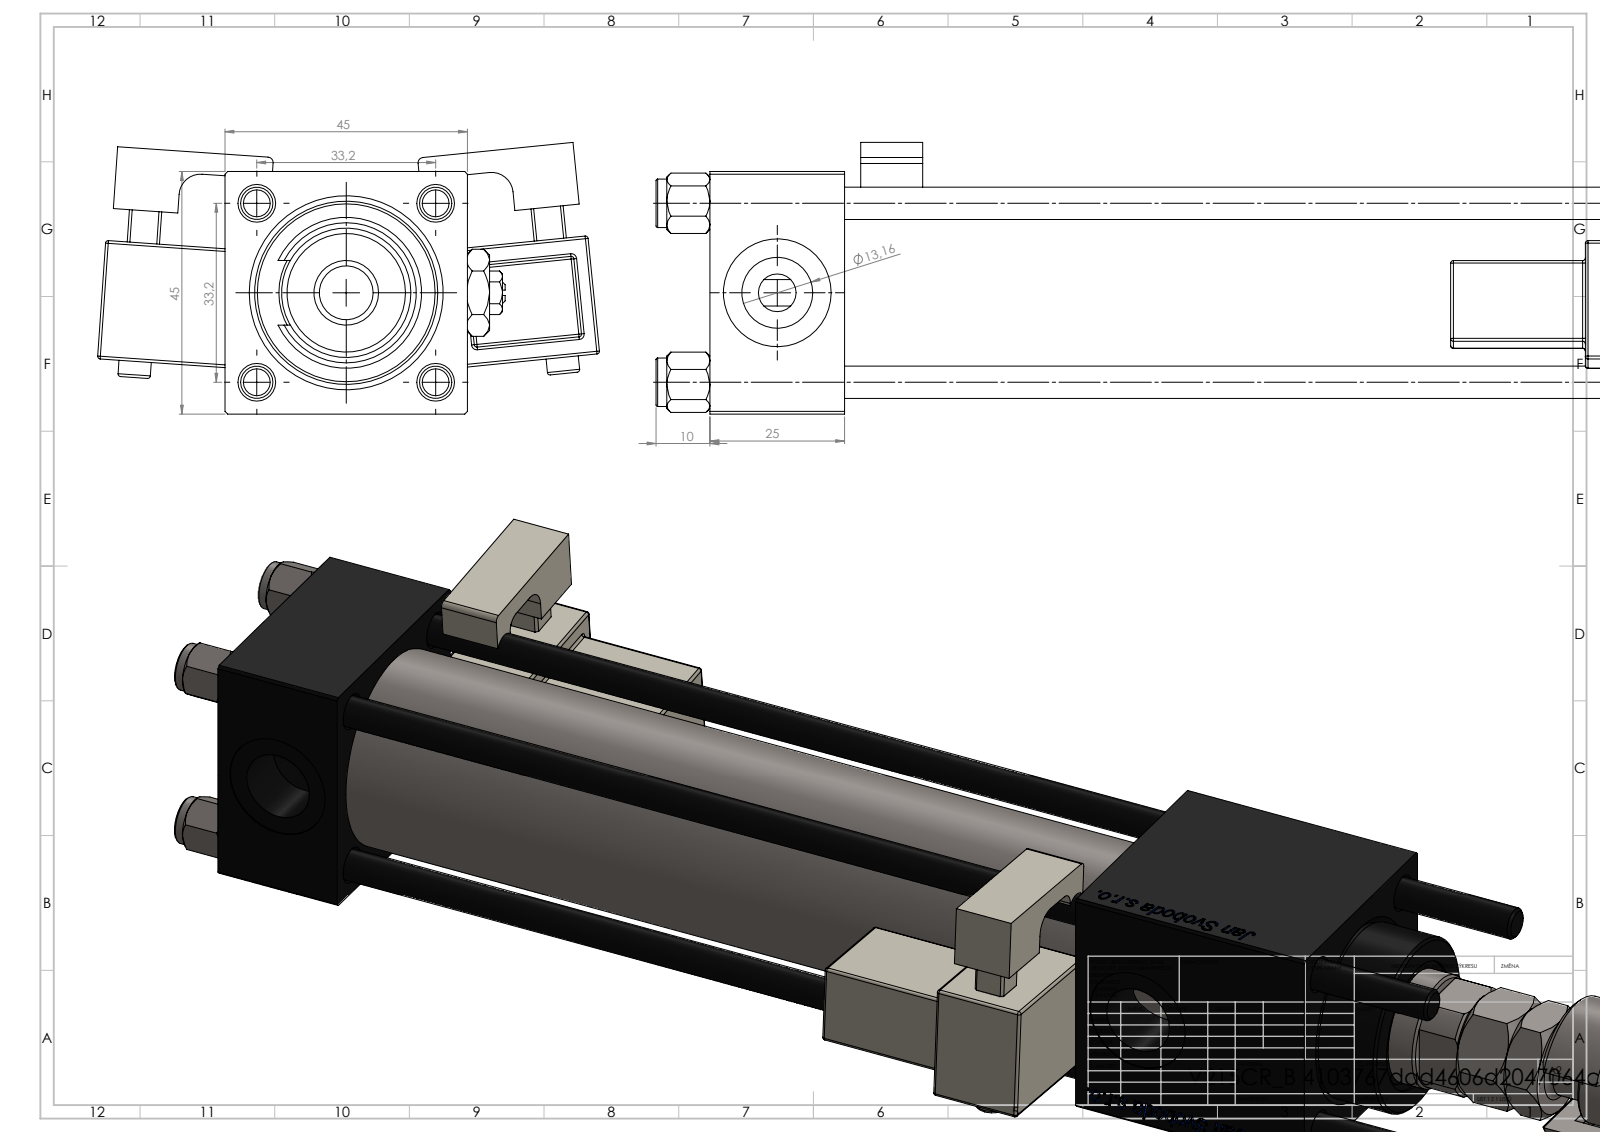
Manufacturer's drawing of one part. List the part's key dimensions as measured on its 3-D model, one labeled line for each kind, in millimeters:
Part name (STEP PRODUCT): V215CR_B_TYCINKA; FEMALE_PART_FOR_DFA; NUT_M5_B; V215CR_VCP_B (+5 more)
STEP written by: SolidWorks 2019 (CONFIG_CONTROL_DESIGN)
Units: millimetres
Bodies: 17 solids, 1499 faces (568 planar, 161 cylindrical, 770 other)
Overall size (bounding box): 324 × 93.14 × 50.4
Volume: 357 744 mm³ · Surface area: 136 016 mm²
Round holes (diameter × count): ⌀6 ×4, ⌀7 ×2, ⌀13.16 ×2, ⌀20 ×2, ⌀10.5 ×1, ⌀22 ×1, ⌀24 ×1, ⌀25 ×1, ⌀32 ×1, ⌀33 ×1
Round bosses / shafts (diameter × count): ⌀9 ×4, ⌀6 ×2, ⌀38 ×1, ⌀34 ×1, ⌀28 ×1, ⌀18 ×1, ⌀12 ×1, ⌀11 ×1
Partial cylindrical surfaces — rounded edges, fillets, slot ends (radius × count): R0.5 ×48, R1 ×2, R2.5 ×2, R4 ×2, R9.75 ×1, R10.5 ×1
Main face-to-face distances: 45, 25, 180, 155, 3, 228, 14.5, 15, 137.5, 17.5
Hole centre spacings: 23.48, 33.2, 46.95, 180.5
